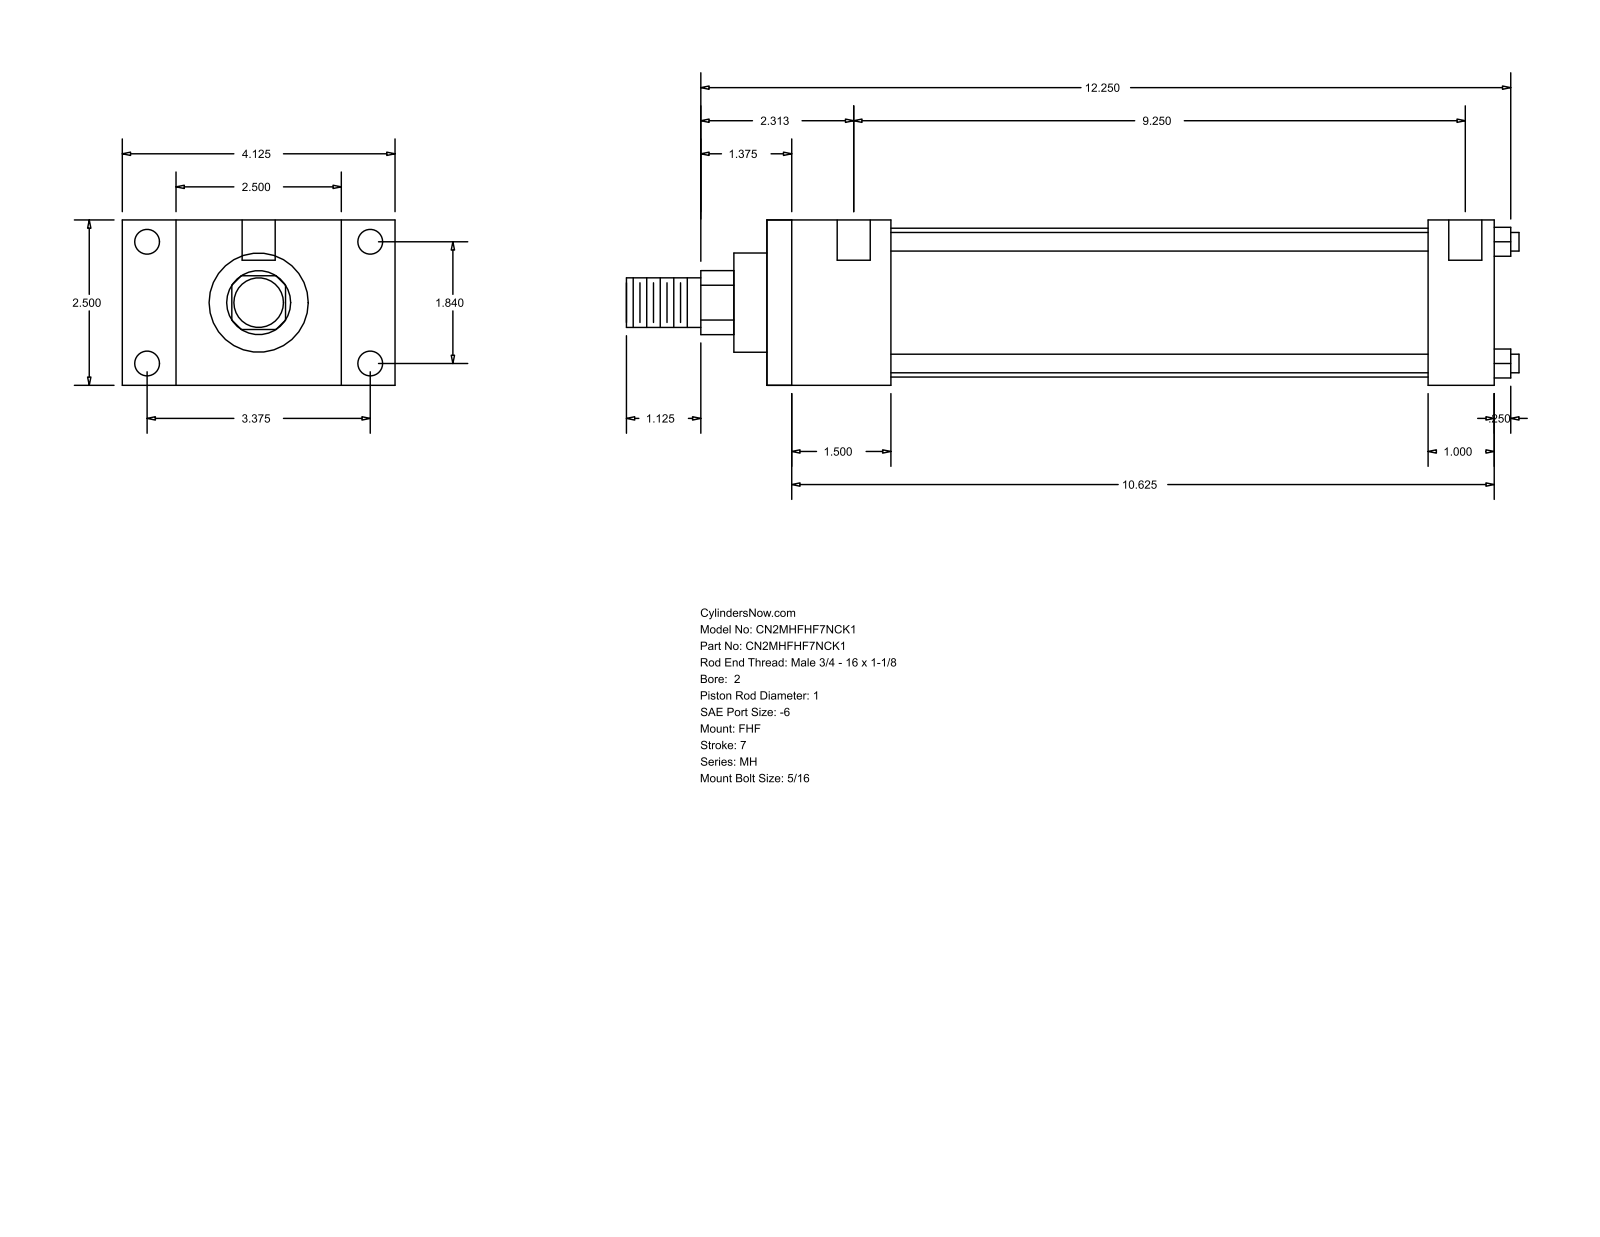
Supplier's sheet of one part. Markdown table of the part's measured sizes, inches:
| quantity | value |
| --- | --- |
| part name | MH_FHF__0200_1 |
| STEP written by | GSSL Pune (CONFIG_CONTROL_DESIGN) |
| units | inches |
| bodies | 0 solids, 88 faces (60 planar, 28 cylindrical, 0 other) |
| overall size | 13.5 × 4.125 × 2.5 |
| round holes (diameter × count) | 0.219 × 4, 0.375 × 4, 0.5 × 2 |
| round bosses / shafts (diameter × count) | 0.281 × 4, 2.25 × 1, 1.5 × 1, 1 × 1, 0.75 × 1 |
| partial cylindrical surfaces (radius × count) | 0.484 × 1 |
| main face-to-face distances | 2.5, 11, 1.875, 9.125, 0.813, 3.313, 4.125, 1, 10, 8.125 |
| hole center spacings | 1.84, 3.375, 3.844, 9.562, 0.125, 0.187, 9.25, 9.375 |
